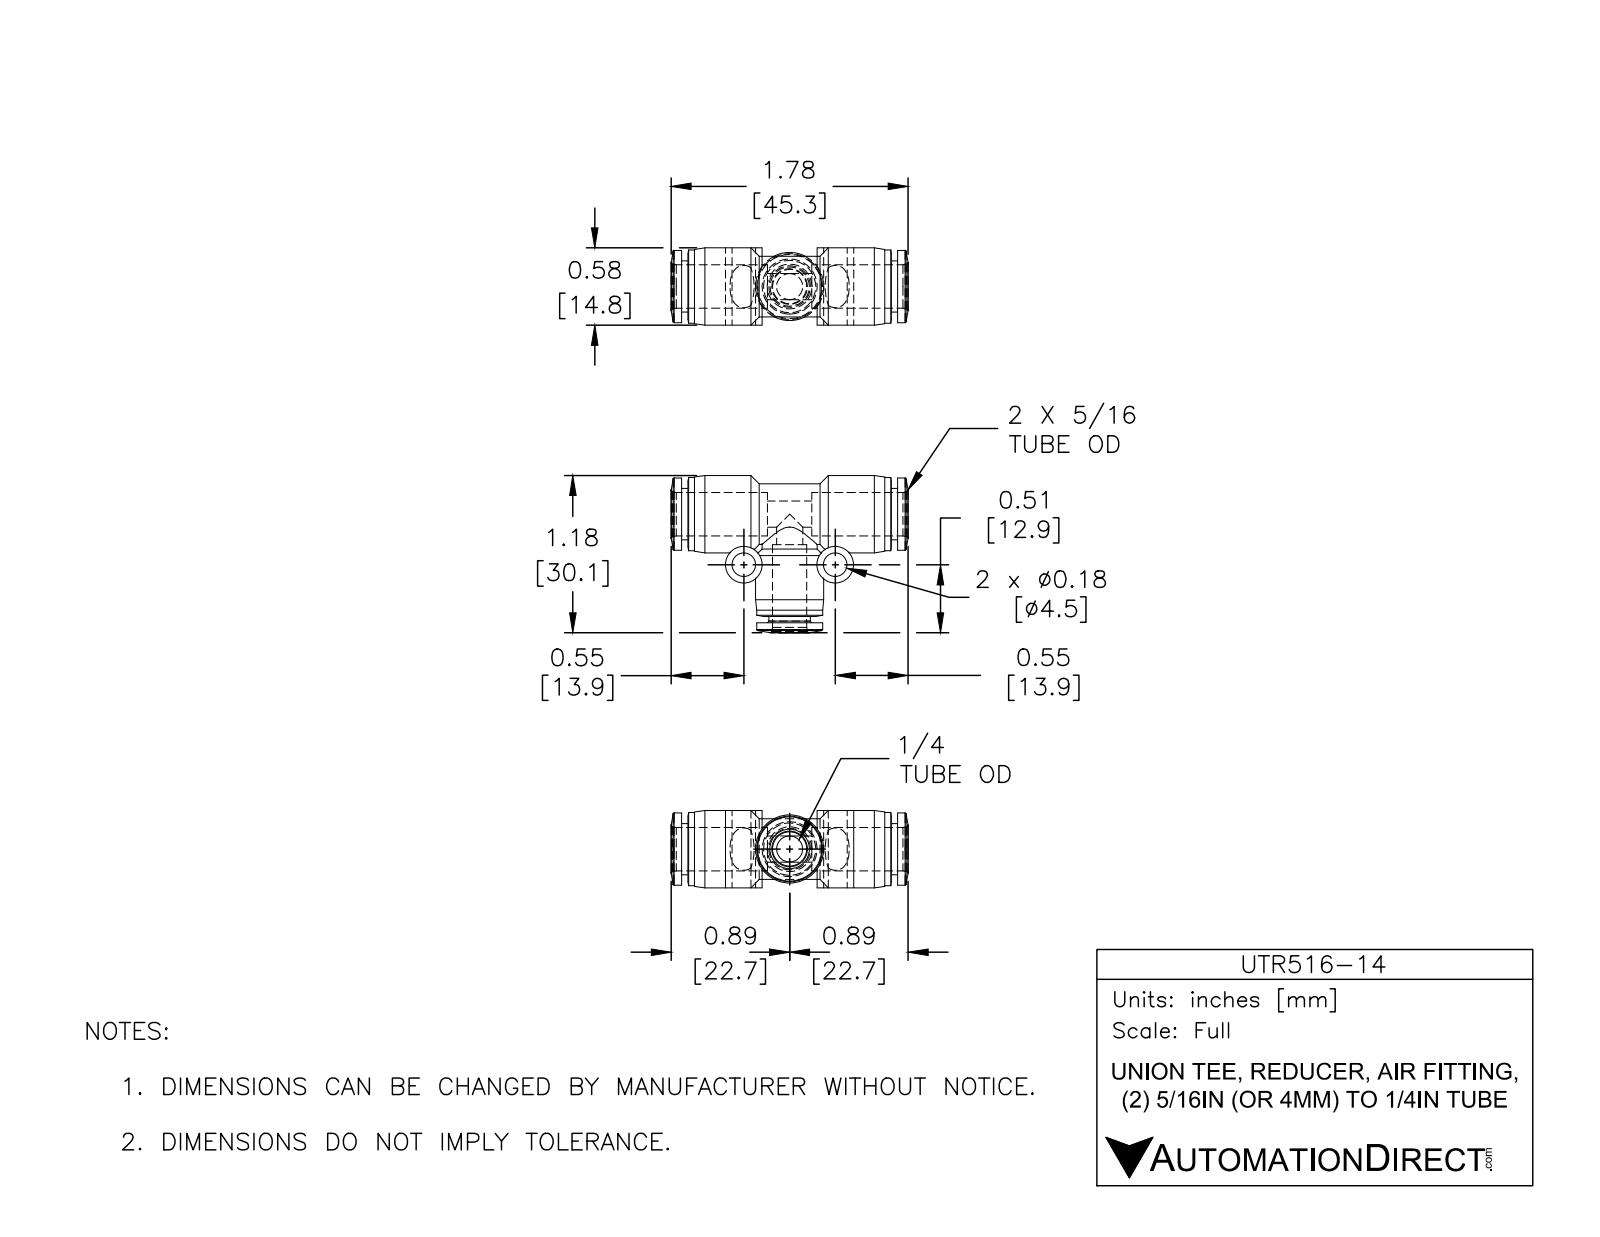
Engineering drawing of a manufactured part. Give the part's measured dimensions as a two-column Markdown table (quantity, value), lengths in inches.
| quantity | value |
| --- | --- |
| part name | UTR516-14 |
| STEP written by | SolidWorks 2015 (CONFIG_CONTROL_DESIGN) |
| units | inches |
| bodies | 1 solid, 105 faces (15 planar, 46 cylindrical, 44 other) |
| overall size | 1.783 × 1.183 × 0.583 |
| volume | 0.386 in³ |
| surface area | 8.828 in² |
| round holes (diameter × count) | 0.177 × 2, 0.197 × 2, 0.258 × 1, 0.327 × 1 |
| round bosses / shafts (diameter × count) | 0.276 × 2, 0.583 × 1, 0.551 × 1, 0.543 × 1, 0.512 × 1, 0.496 × 1, 0.457 × 1, 0.413 × 1 |
| main face-to-face distances | 0.047, 1.579, 1.626, 0.646, 0.98, 0.598, 0.933, 1.531, 0.583, 0.335 |
| hole center spacings | 0.689 |
